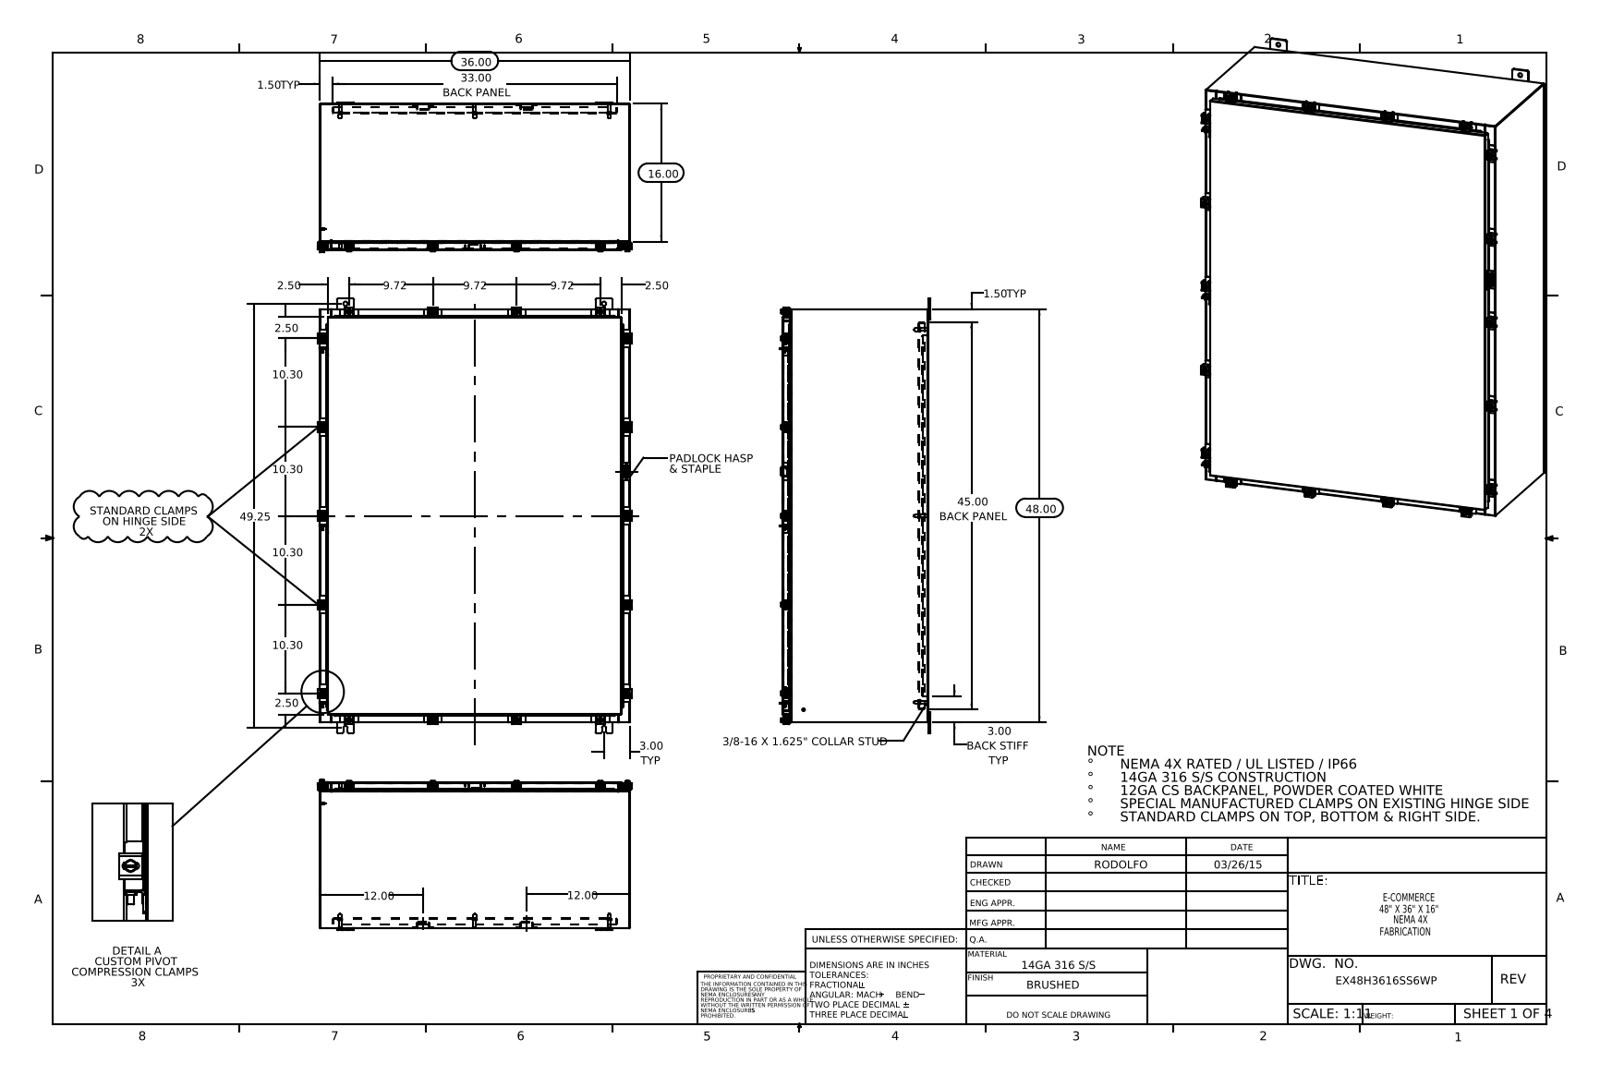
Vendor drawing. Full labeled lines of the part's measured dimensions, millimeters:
Part name (STEP PRODUCT): EX48H3616SS6WP; N-WMT04X30402202210-00 22101002; EX48H3616SS6WP Top; 22101002_RTP29 (+8 more)
STEP written by: SolidWorks 2014 (CONFIG_CONTROL_DESIGN)
Units: millimetres
Bodies: 126 solids, 3106 faces (1613 planar, 1195 cylindrical, 298 other)
Overall size (bounding box): 1282.7 × 925.1 × 443.3
Volume: 11 450 000 mm³ · Surface area: 11 280 000 mm²
Round holes (diameter × count): ⌀5.4 ×18, ⌀6.6 ×18, ⌀12.7 ×12, ⌀6.4 ×7, ⌀3.2 ×1
Round bosses / shafts (diameter × count): ⌀12.7 ×18, ⌀6.4 ×18, ⌀10.1 ×15, ⌀15.9 ×8, ⌀9.5 ×8, ⌀8.4 ×8, ⌀4 ×6, ⌀3.6 ×6
Partial cylindrical surfaces — rounded edges, fillets, slot ends (radius × count): R1.5 ×76, R0.3 ×38, R3.6 ×36, R2.2 ×34, R3 ×33, R2.3 ×27, R1.3 ×25, R3.7 ×24
Main face-to-face distances: 1.9, 429.3, 427.4, 431.2, 2.6, 912.5, 25.4, 27.3, 402, 403.9
Hole centre spacings: 50, 59.6, 112.8, 354.9, 374.1, 409.6, 422.2, 451
